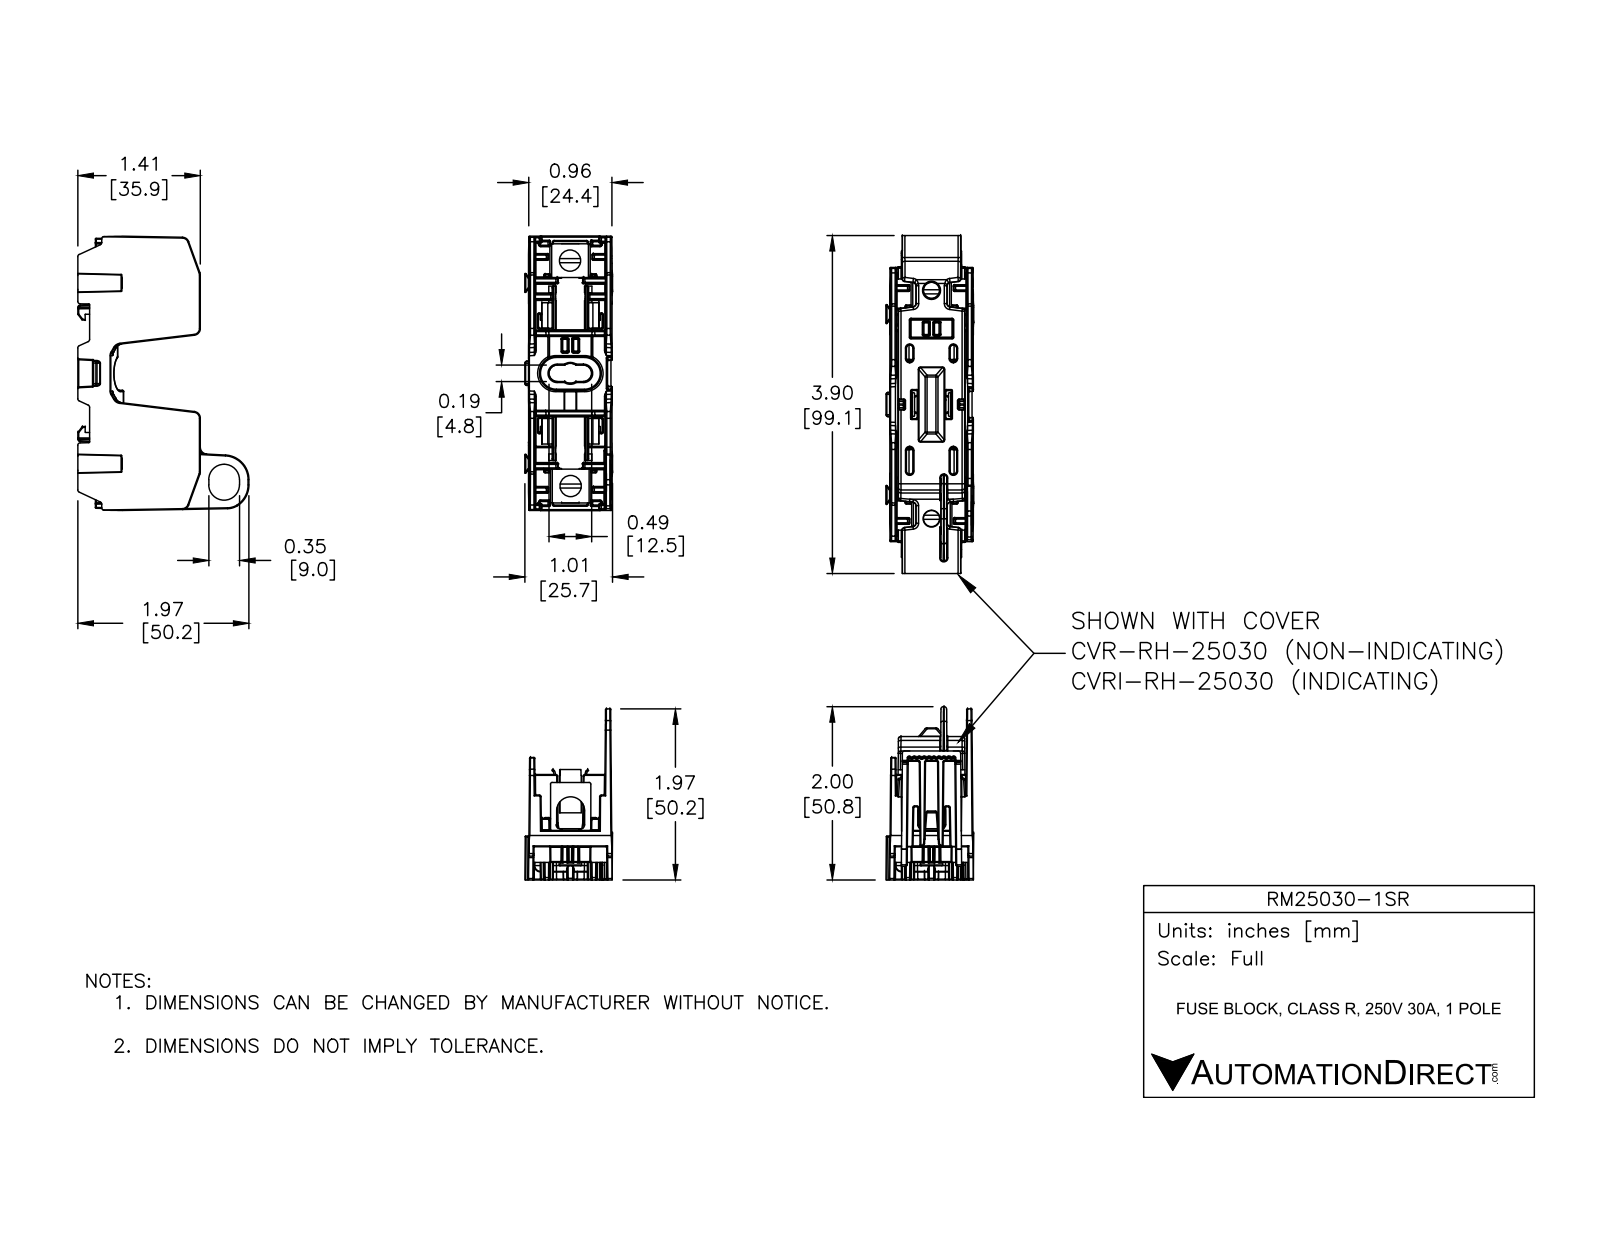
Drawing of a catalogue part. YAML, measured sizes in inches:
part_name: "RM25030-1SR"
step_written_by: "SolidWorks 2016 (AUTOMOTIVE_DESIGN)"
units: inches
bodies: {solids: 11, faces: 2901, planar: 650, cylindrical: 1230, other: 1021}
overall_size: [3.165, 1.974, 1.013]
volume: 1.42
surface_area: 37.6
round_holes:
  - {diameter: 0.142, count: 2}
  - {diameter: 0.244, count: 2}
round_bosses_or_shafts:
  - {diameter: 0.244, count: 2}
partial_cylinders:
  - {radius: 0.01, count: 430}
  - {radius: 0.006, count: 264}
  - {radius: 0.02, count: 71}
  - {radius: 0.03, count: 17}
  - {radius: 0.079, count: 17}
  - {radius: 0.02, count: 16}
  - {radius: 0.045, count: 11}
  - {radius: 0.069, count: 8}
face_to_face_distances: [0.881, 0.059, 0.344, 0.369, 0.025, 0.025, 0.041, 0.017, 0.813, 0.822]
hole_center_spacings: [0.552, 2.048, 1.496, 2.601]
